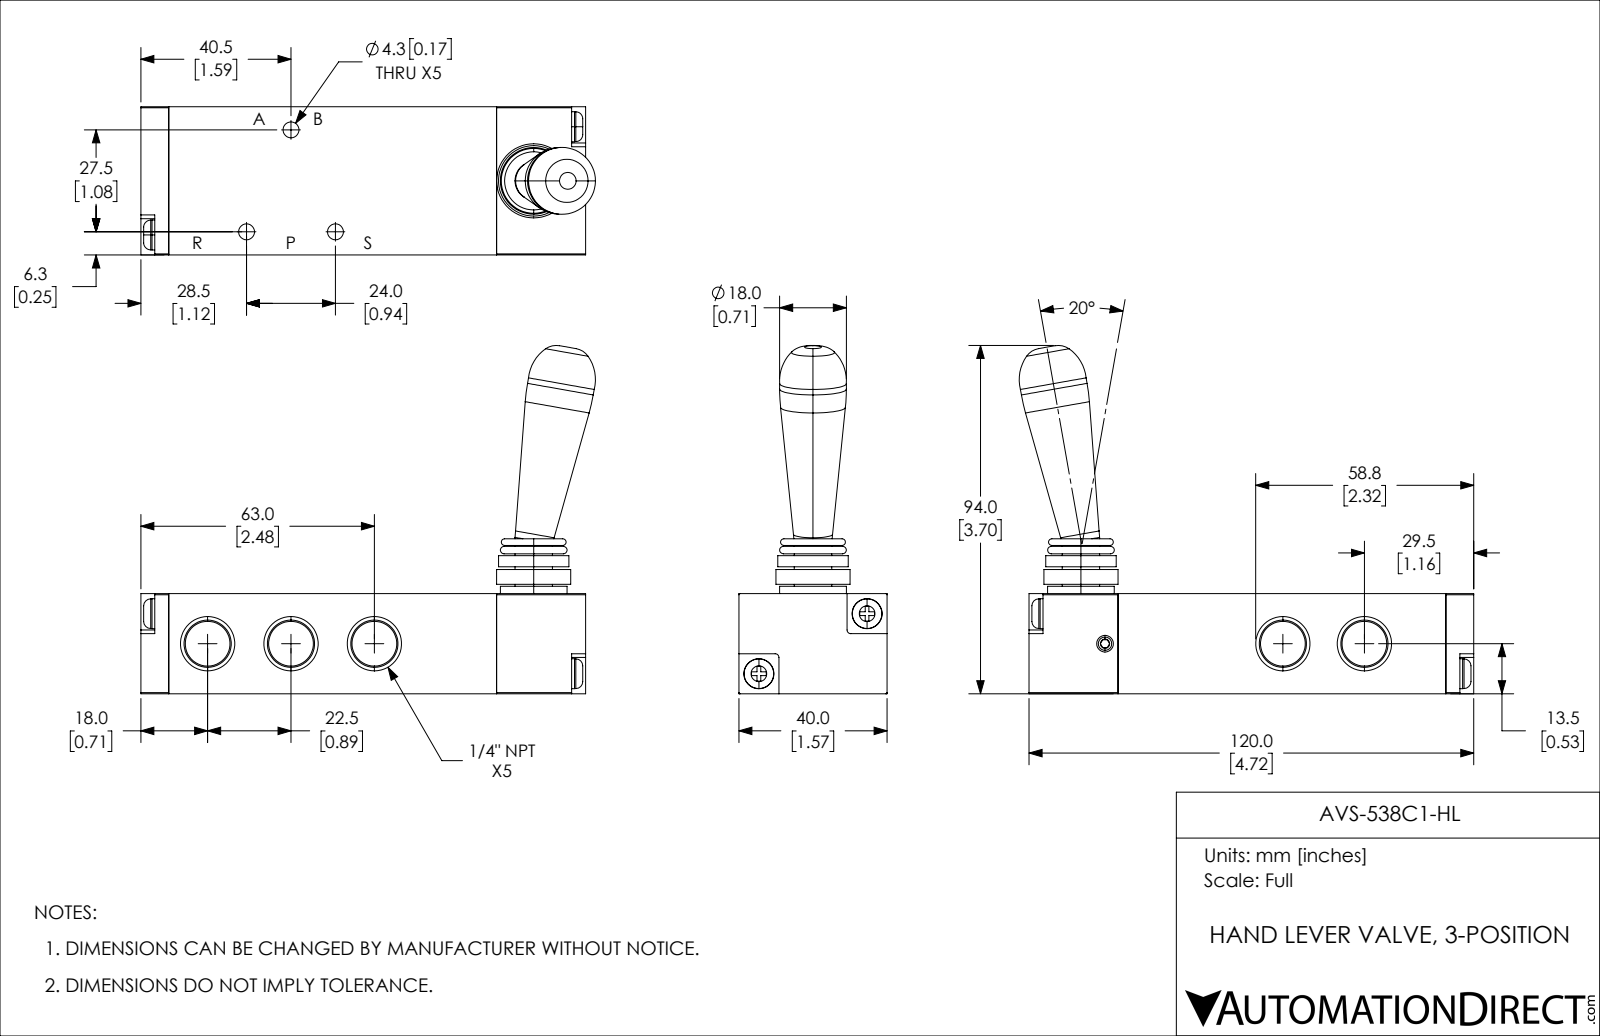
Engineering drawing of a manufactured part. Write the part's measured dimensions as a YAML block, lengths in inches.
part_name: "AVS-538C1-HL"
step_written_by: "SolidWorks 2018 (AUTOMOTIVE_DESIGN)"
units: inches
bodies: {solids: 4, faces: 219, planar: 118, cylindrical: 57, other: 44}
overall_size: [4.829, 3.699, 1.575]
volume: 8.069
surface_area: 48.98
round_holes:
  - {diameter: 0.169, count: 3}
  - {diameter: 0.177, count: 1}
  - {diameter: 0.709, count: 1}
round_bosses_or_shafts:
  - {diameter: 0.319, count: 4}
  - {diameter: 0.315, count: 4}
  - {diameter: 0.787, count: 1}
  - {diameter: 0.748, count: 1}
  - {diameter: 0.709, count: 1}
  - {diameter: 0.398, count: 1}
  - {diameter: 0.142, count: 1}
partial_cylinders:
  - {radius: 0.012, count: 4}
  - {radius: 0.039, count: 4}
face_to_face_distances: [1.063, 1.575, 3.484, 4.429, 0.945, 4.724, 3.78, 0.295, 0.079, 0.157]
hole_center_spacings: [1.181, 0.945, 2.175, 2.635, 3.099]
